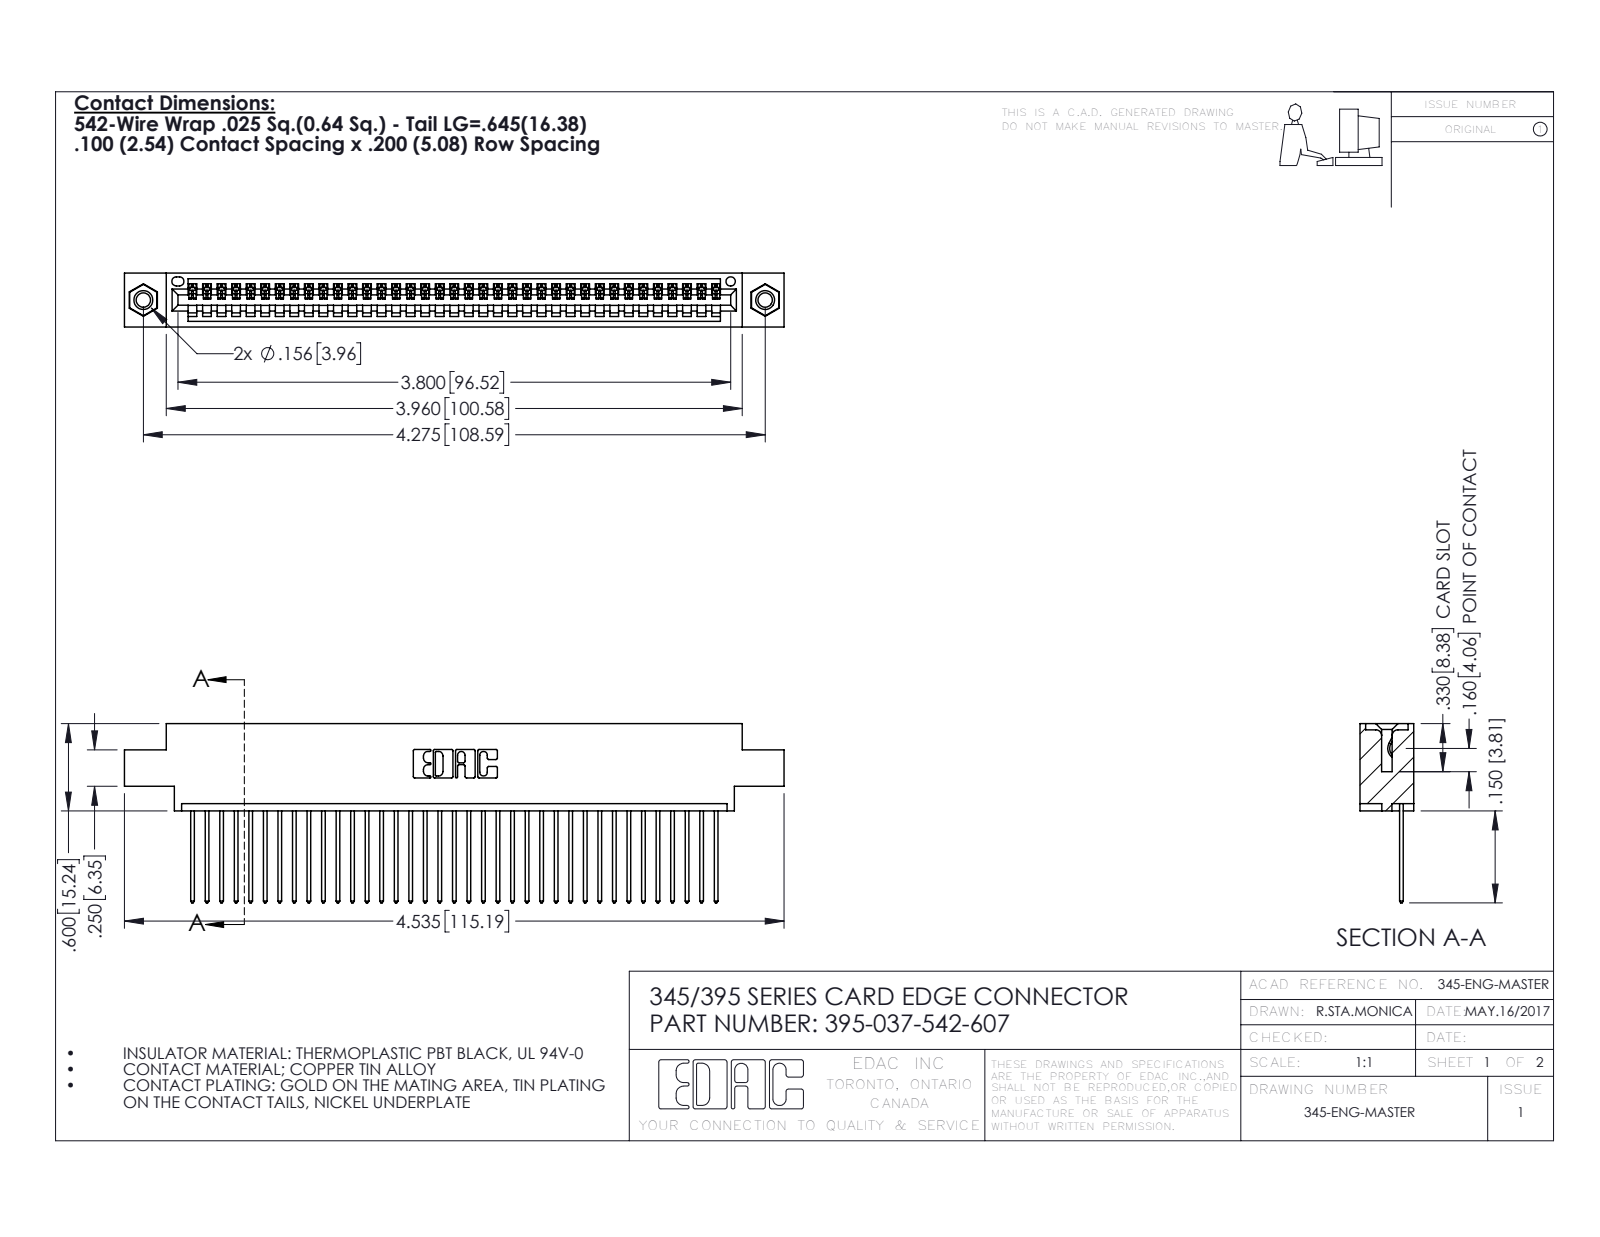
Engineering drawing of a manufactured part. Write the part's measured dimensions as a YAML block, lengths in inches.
part_name: "395-037-542-607; 345-292-001_345-293-142; 345-250-001_345-250-005-103; 345 Part_0.170 Offset - 0.156 Dia-TI"
step_written_by: "SolidWorks 2016 (CONFIG_CONTROL_DESIGN)"
units: inches
bodies: {solids: 40, faces: 2336, planar: 1596, cylindrical: 724, other: 16}
overall_size: [4.535, 1.232, 0.37]
volume: 0.662
surface_area: 23.31
round_holes:
  - {diameter: 0.098, count: 2}
  - {diameter: 0.125, count: 2}
  - {diameter: 0.156, count: 2}
  - {diameter: 0.064, count: 1}
round_bosses_or_shafts:
  - {diameter: 0.155, count: 2}
partial_cylinders:
  - {radius: 0.006, count: 74}
  - {radius: 0.01, count: 74}
  - {radius: 0.01, count: 22}
  - {radius: 0.007, count: 6}
  - {radius: 0.031, count: 6}
  - {radius: 0.026, count: 3}
  - {radius: 0.031, count: 2}
  - {radius: 0.04, count: 2}
face_to_face_distances: [0.072, 0.298, 0.37, 0.098, 0.272, 0.025, 0.2, 0.225, 0.175, 0.149]
hole_center_spacings: [0.27, 4.039, 4.275]
